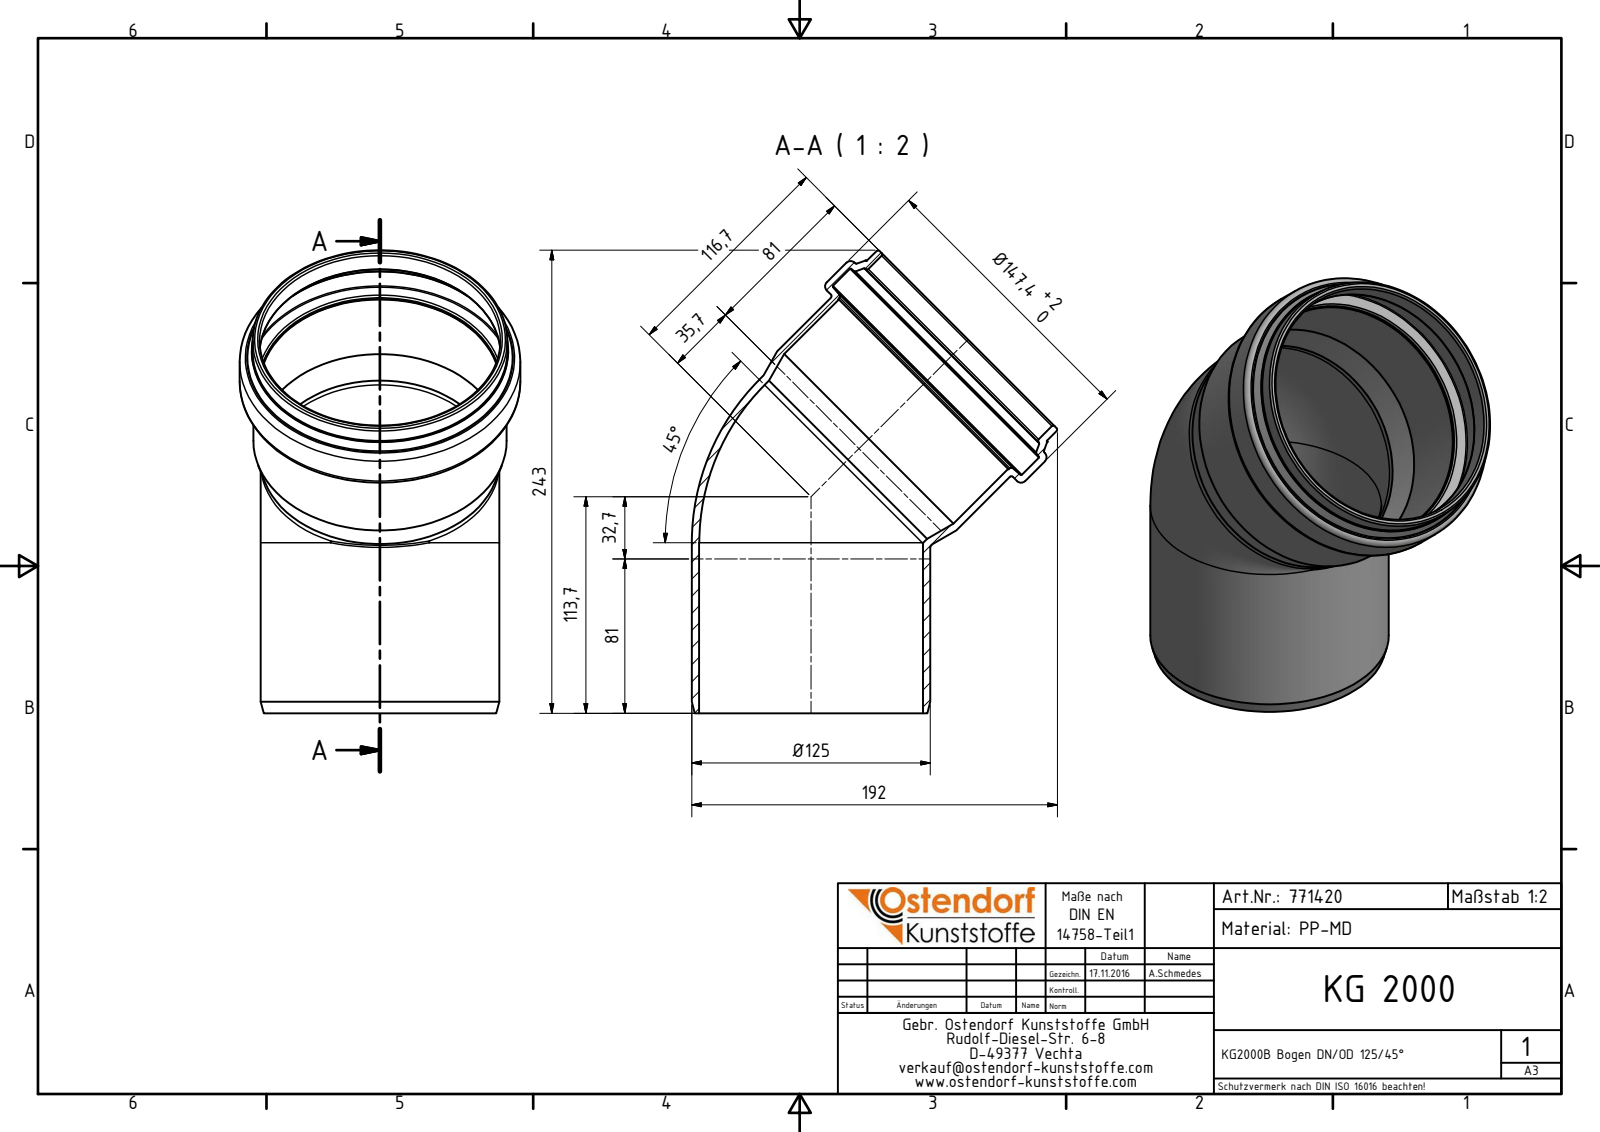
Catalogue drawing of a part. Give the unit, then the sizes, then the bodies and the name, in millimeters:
Units: millimetres
Overall size (bounding box): 243 × 192 × 147.4
Round holes (diameter × count): ⌀117.1 ×2, ⌀126.5 ×2, ⌀125.8 ×1, ⌀140.2 ×1
Round bosses / shafts (diameter × count): ⌀125.3 ×2, ⌀147.4 ×1, ⌀133.7 ×1, ⌀133 ×1
Main face-to-face distances: 34.3, 20.7, 13.6, 1.17, 19.53, 33.13, 54.88, 56.05, 75.58, 89.18
Volume: 347 774 mm³ · Surface area: 190 351 mm²
Bodies: 1 solid, 43 faces (6 planar, 11 cylindrical, 26 other)
Part name (STEP PRODUCT): 771420 KG2000B Bogen DN_OD 125_45°
STEP written by: Autodesk Inventor 2016 (AUTOMOTIVE_DESIGN)
